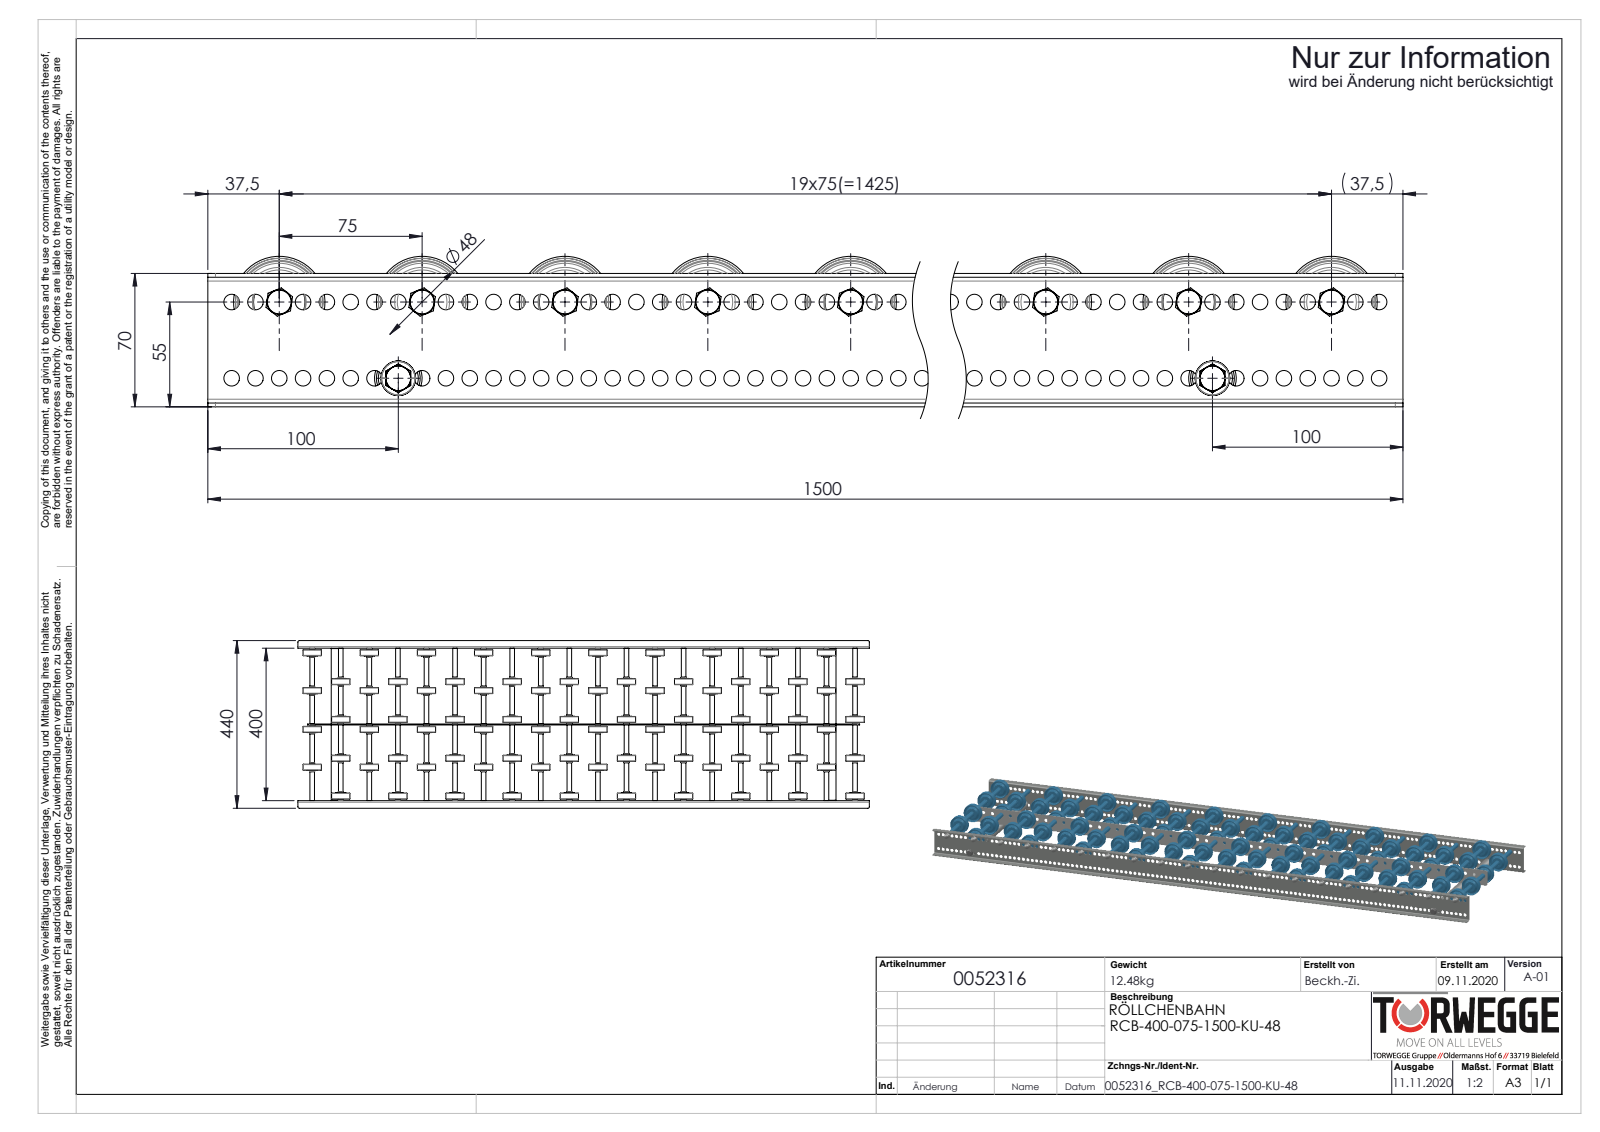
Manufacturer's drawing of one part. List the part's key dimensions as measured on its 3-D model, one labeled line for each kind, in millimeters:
Part name (STEP PRODUCT): Profil_LRB-20x70x20x2_KFG_S100201_U-PROFIL-20-70-20-2-LRB-L=1500; Röllchenachse-für-Konfiguration_EL400; S106837_Gewindestange-M8-KFG_L420; 0052316 (+6 more)
STEP written by: SolidWorks 2020 (AUTOMOTIVE_DESIGN)
Units: millimetres
Bodies: 233 solids, 8638 faces (1526 planar, 3088 cylindrical, 4024 other)
Overall size (bounding box): 1500 × 440 × 79
Volume: 3 086 000 mm³ · Surface area: 2 296 000 mm²
Round holes (diameter × count): ⌀8.2 ×238, ⌀8.5 ×58, ⌀6.65 ×20, ⌀9.65 ×20, ⌀13.7 ×20, ⌀6.8 ×2, ⌀21 ×2
Round bosses / shafts (diameter × count): ⌀8 ×22, ⌀48 ×20, ⌀27 ×20, ⌀12.7 ×20, ⌀12.5 ×20, ⌀12 ×20, ⌀25 ×2
Partial cylindrical surfaces — rounded edges, fillets, slot ends (radius × count): R4 ×8, R2 ×4, R5 ×4
Main face-to-face distances: 2, 402, 68, 404, 400, 201.1, 198.6, 203.4, 200.9, 198.9
Hole centre spacings: 12.5, 25, 37.5, 50, 62.5, 75, 87.5, 100
